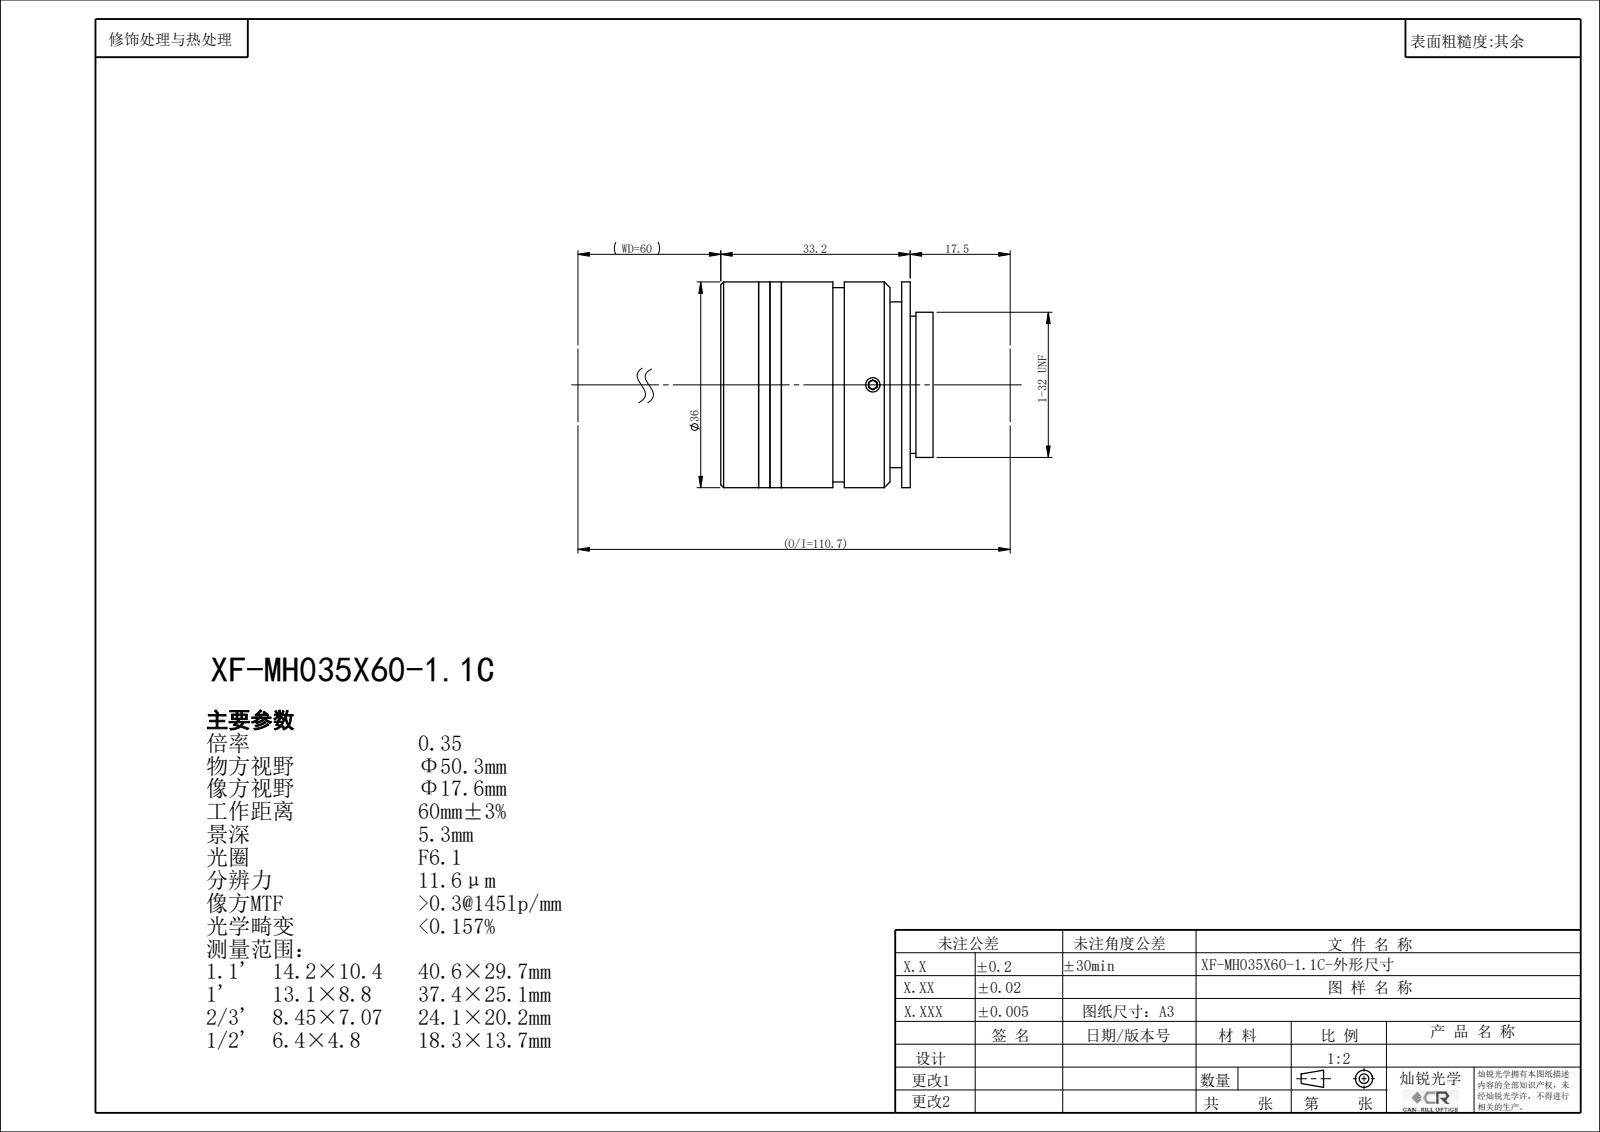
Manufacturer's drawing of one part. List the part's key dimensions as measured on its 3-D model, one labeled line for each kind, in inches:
Part name (STEP PRODUCT): XF-MH035X60-1.1C
STEP written by: SolidWorks 2022 (CONFIG_CONTROL_DESIGN)
Units: inches
Bodies: 0 solids, 110 faces (51 planar, 38 cylindrical, 21 other)
Overall size (bounding box): 1.463 × 1.417 × 1.417
Round holes (diameter × count): ⌀0.098 ×3, ⌀0.394 ×1, ⌀0.591 ×1, ⌀0.685 ×1, ⌀0.846 ×1, ⌀0.98 ×1, ⌀1.024 ×1
Round bosses / shafts (diameter × count): ⌀1.417 ×1, ⌀1.339 ×1, ⌀1.142 ×1, ⌀1 ×1, ⌀0.945 ×1
Main face-to-face distances: 0.079, 0.157, 1.045, 0.967, 0.888, 0.261, 0.339, 0.418, 1.306, 0.059
